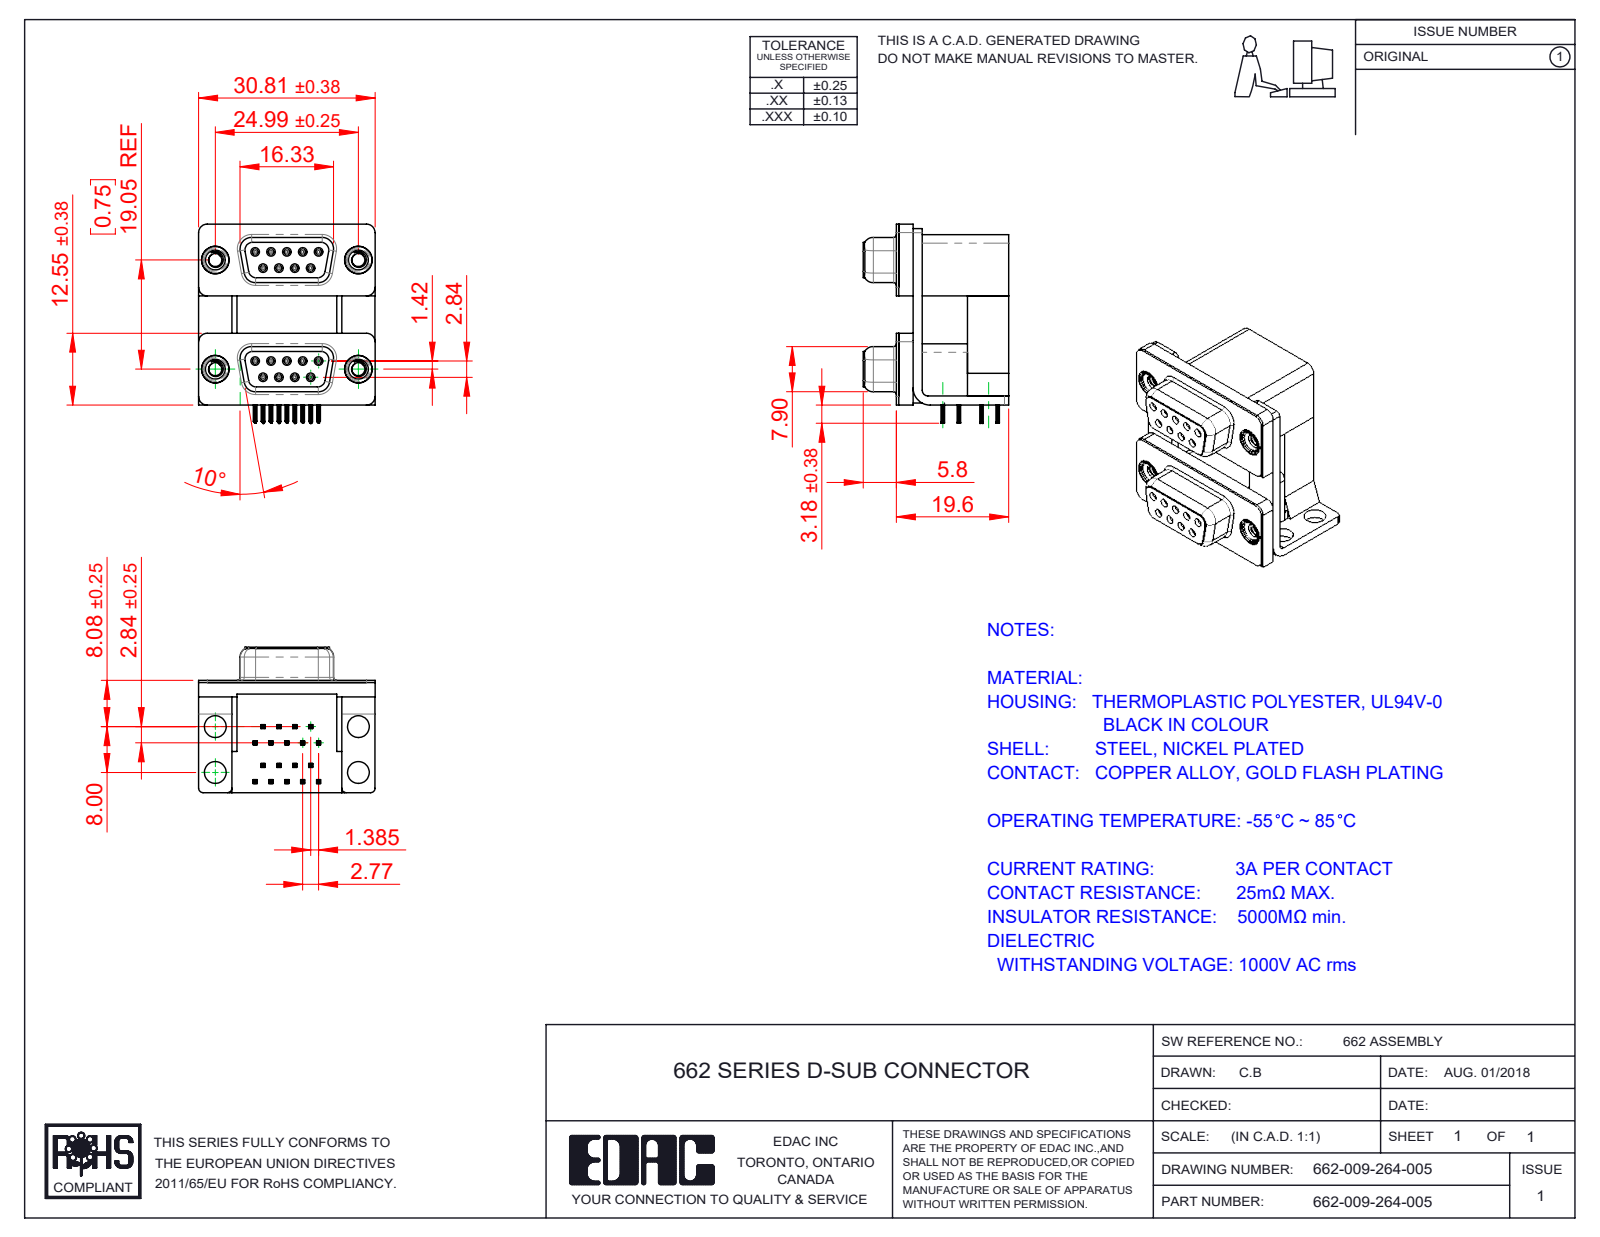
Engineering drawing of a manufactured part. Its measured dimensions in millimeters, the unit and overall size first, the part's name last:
Units: millimetres
Overall size (bounding box): 34.78 × 30.81 × 25.4
Round holes (diameter × count): ⌀0.8 ×18, ⌀0.9 ×18, ⌀2.26 ×4, ⌀3.5 ×4, ⌀3.8 ×4, ⌀4 ×4, ⌀4.8 ×4, ⌀5 ×4
Round bosses / shafts (diameter × count): ⌀1.2 ×18, ⌀4.9 ×4, ⌀4.75 ×4, ⌀3.9 ×4
Partial cylindrical surfaces — rounded edges, fillets, slot ends (radius × count): R0.1 ×144, R0.15 ×72, R0.35 ×36, R0.34 ×18, R1.35 ×16, R1.5 ×12, R0.28 ×8, R0.5 ×8
Main face-to-face distances: 2.5, 0.4, 16.7, 19.2, 19.05, 2.9, 12, 12.4, 7.2, 9.5
Hole centre spacings: 3.16, 2.77, 19.25, 19.05, 5.54, 19.84, 16.27, 21.93
Volume: 11 281 mm³ · Surface area: 13 173 mm²
Bodies: 29 solids, 3110 faces (1374 planar, 796 cylindrical, 940 other)
Part name (STEP PRODUCT): 662 Housing Upper_09 Contacts M; 662 Contact Bottom Lower; 662-009-264-005; 662 Shell_09 Contacts (+7 more)
STEP written by: SolidWorks 2020 (CONFIG_CONTROL_DESIGN)
